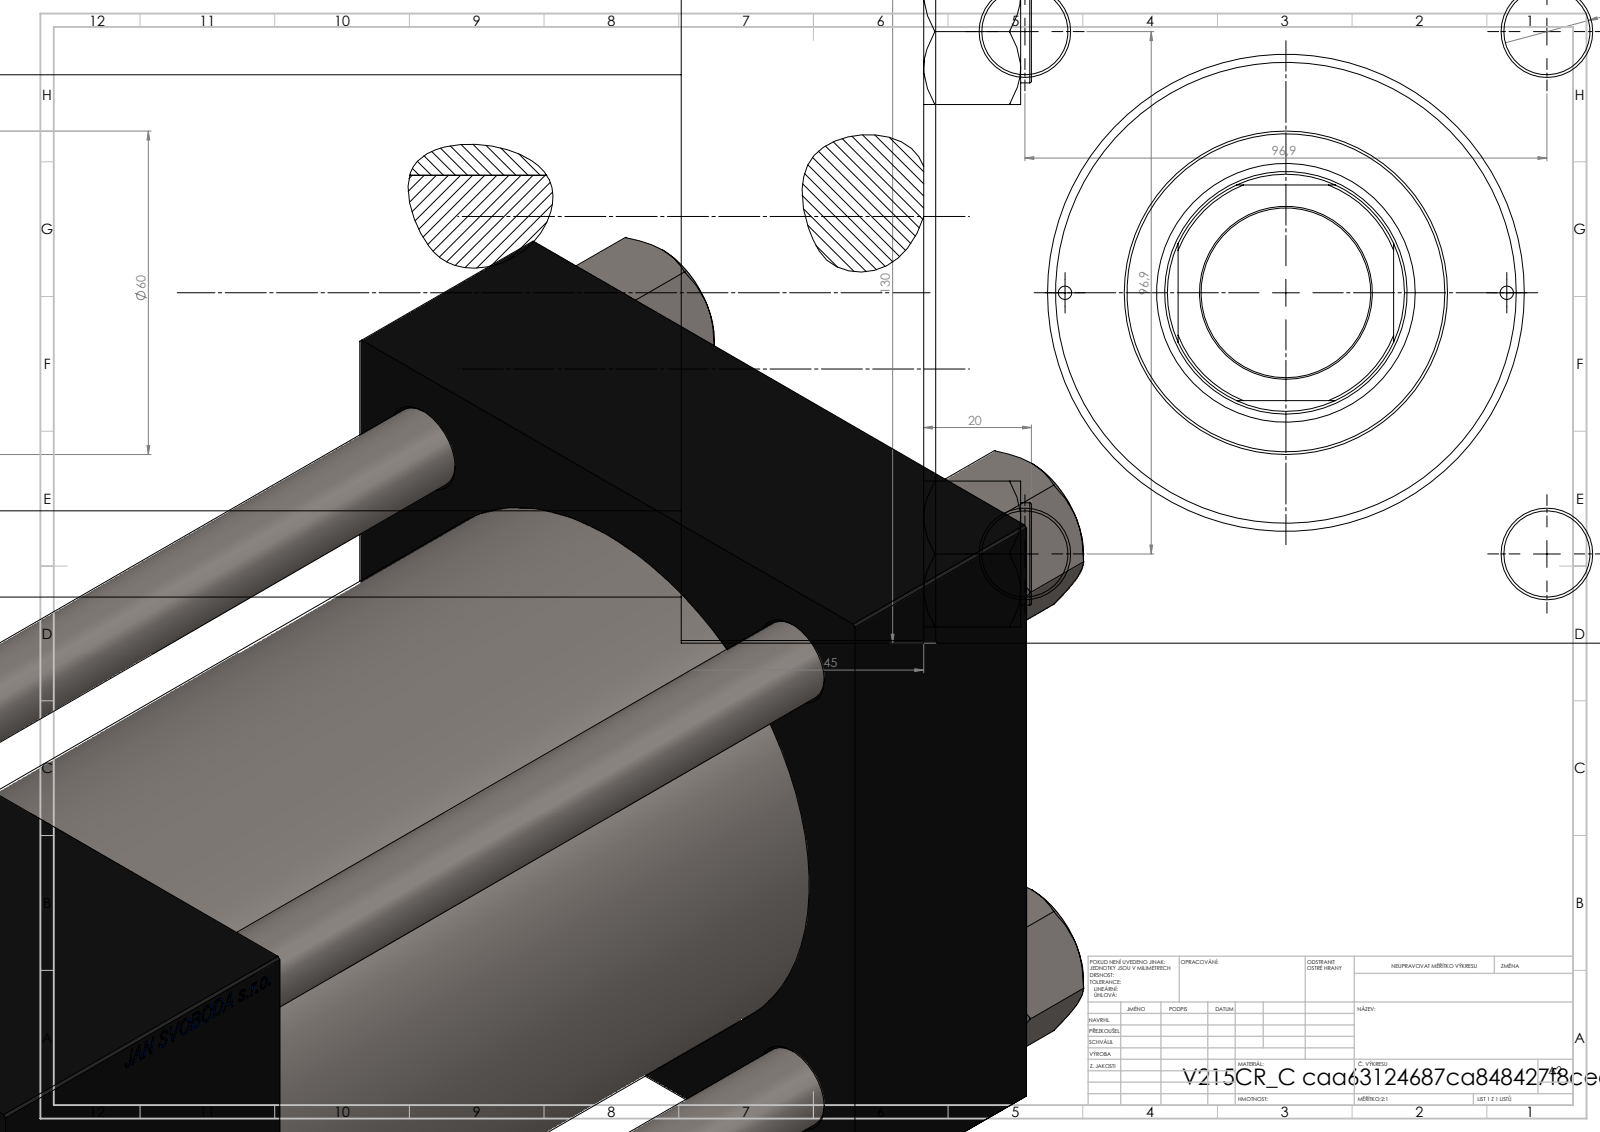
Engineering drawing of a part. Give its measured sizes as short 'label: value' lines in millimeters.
name: NUT_M5_C; V215CR_VCP_C; V215CR_C_TYCINKA; V215CR_C_Body (+1 more)
written by: SolidWorks 2019 (CONFIG_CONTROL_DESIGN)
unit: mm
bodies: 11 solids, 1202 faces (576 planar, 90 cylindrical, 536 other)
size: 323 × 130 × 130
volume: 2 694 000 mm³; area: 405 634 mm²
holes: 4× ⌀16, 2× ⌀2.5, 2× ⌀7, 2× ⌀26.44, 2× ⌀35, 1× ⌀31.5, 1× ⌀45, 1× ⌀48, 1× ⌀76, 1× ⌀85.5, 1× ⌀100
bosses: 4× ⌀19, 1× ⌀106, 1× ⌀60
rounds: 1× R22
face distances: 130, 45, 268, 223, 196, 151, 72, 96, 51, 100
hole spacings: 49.02, 68.52, 96.9, 101.73, 41, 137.04, 82, 198.5
